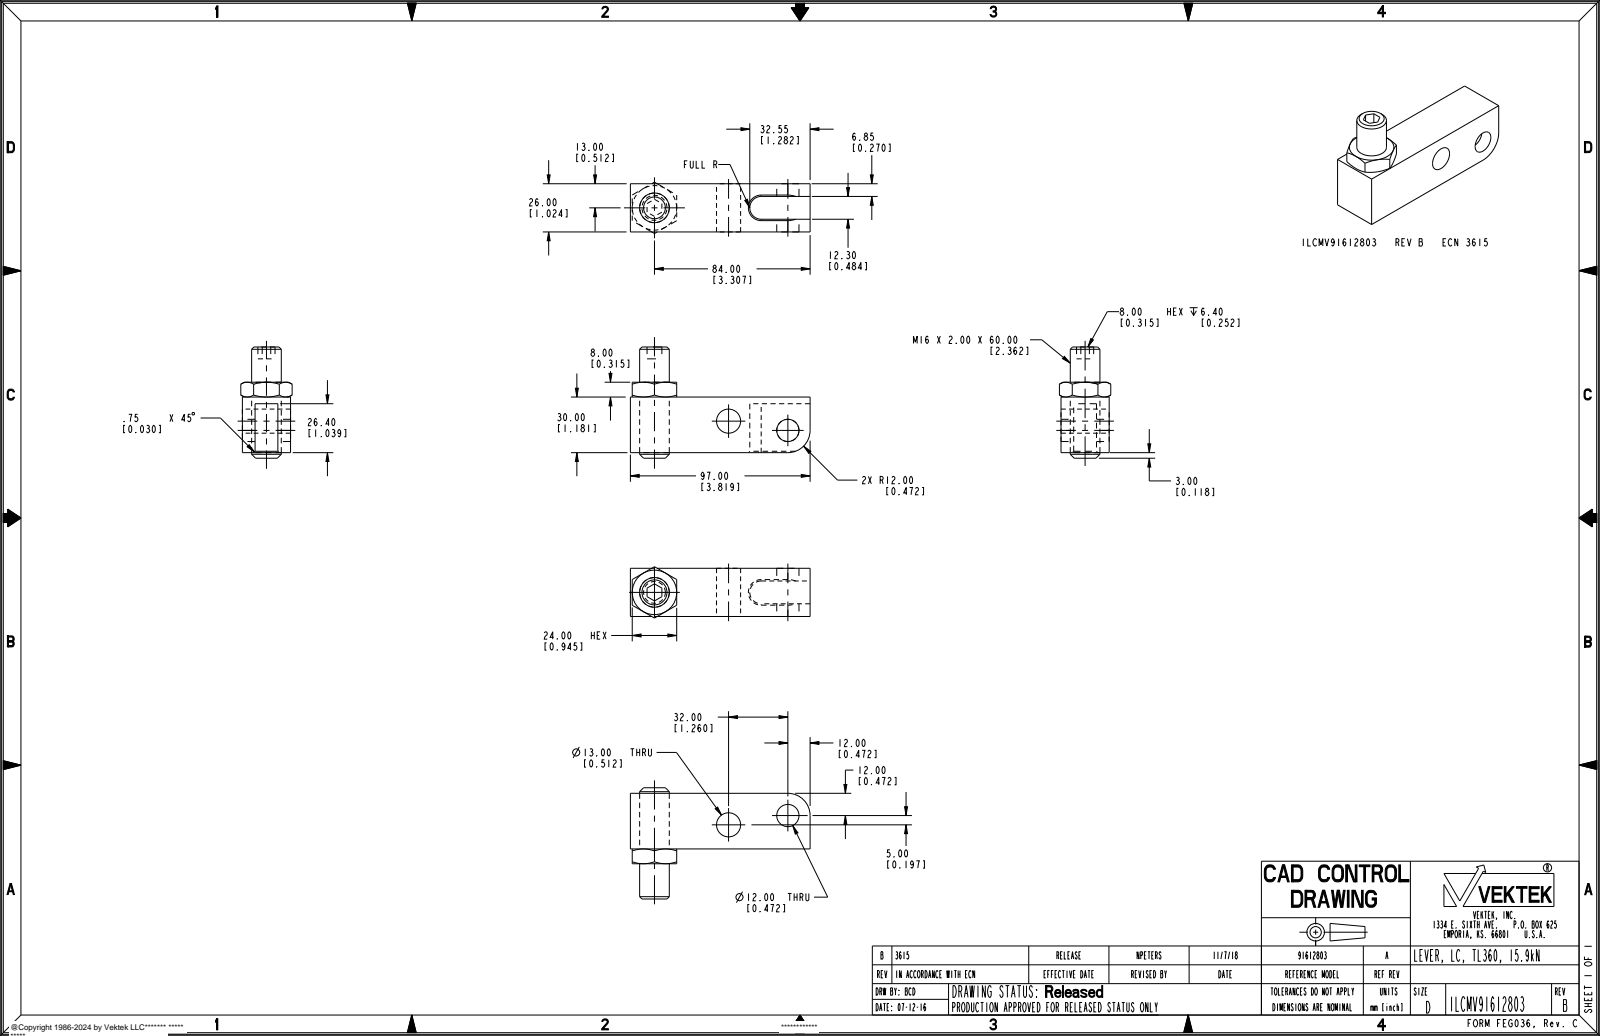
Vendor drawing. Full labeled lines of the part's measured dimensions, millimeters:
Part name (STEP PRODUCT): ILCMV91612803
STEP written by: PRO/ENGINEER BY PARAMETRIC TECHNOLOGY CORPORATION, 2013320 (AUTOMOTIVE_DESIGN)
Units: millimetres
Bodies: 1 solid, 59 faces (27 planar, 15 cylindrical, 17 other)
Overall size (bounding box): 97 × 60 × 27.71
Volume: 67 969 mm³ · Surface area: 18 041 mm²
Round holes (diameter × count): ⌀12 ×1, ⌀13 ×1
Round bosses / shafts (diameter × count): ⌀16 ×1
Partial cylindrical surfaces — rounded edges, fillets, slot ends (radius × count): R6.15 ×1, R12 ×1
Main face-to-face distances: 26, 30, 6.85, 19.15, 12.3, 8, 26.4, 3.6, 24, 97
Hole centre spacings: 32.39
